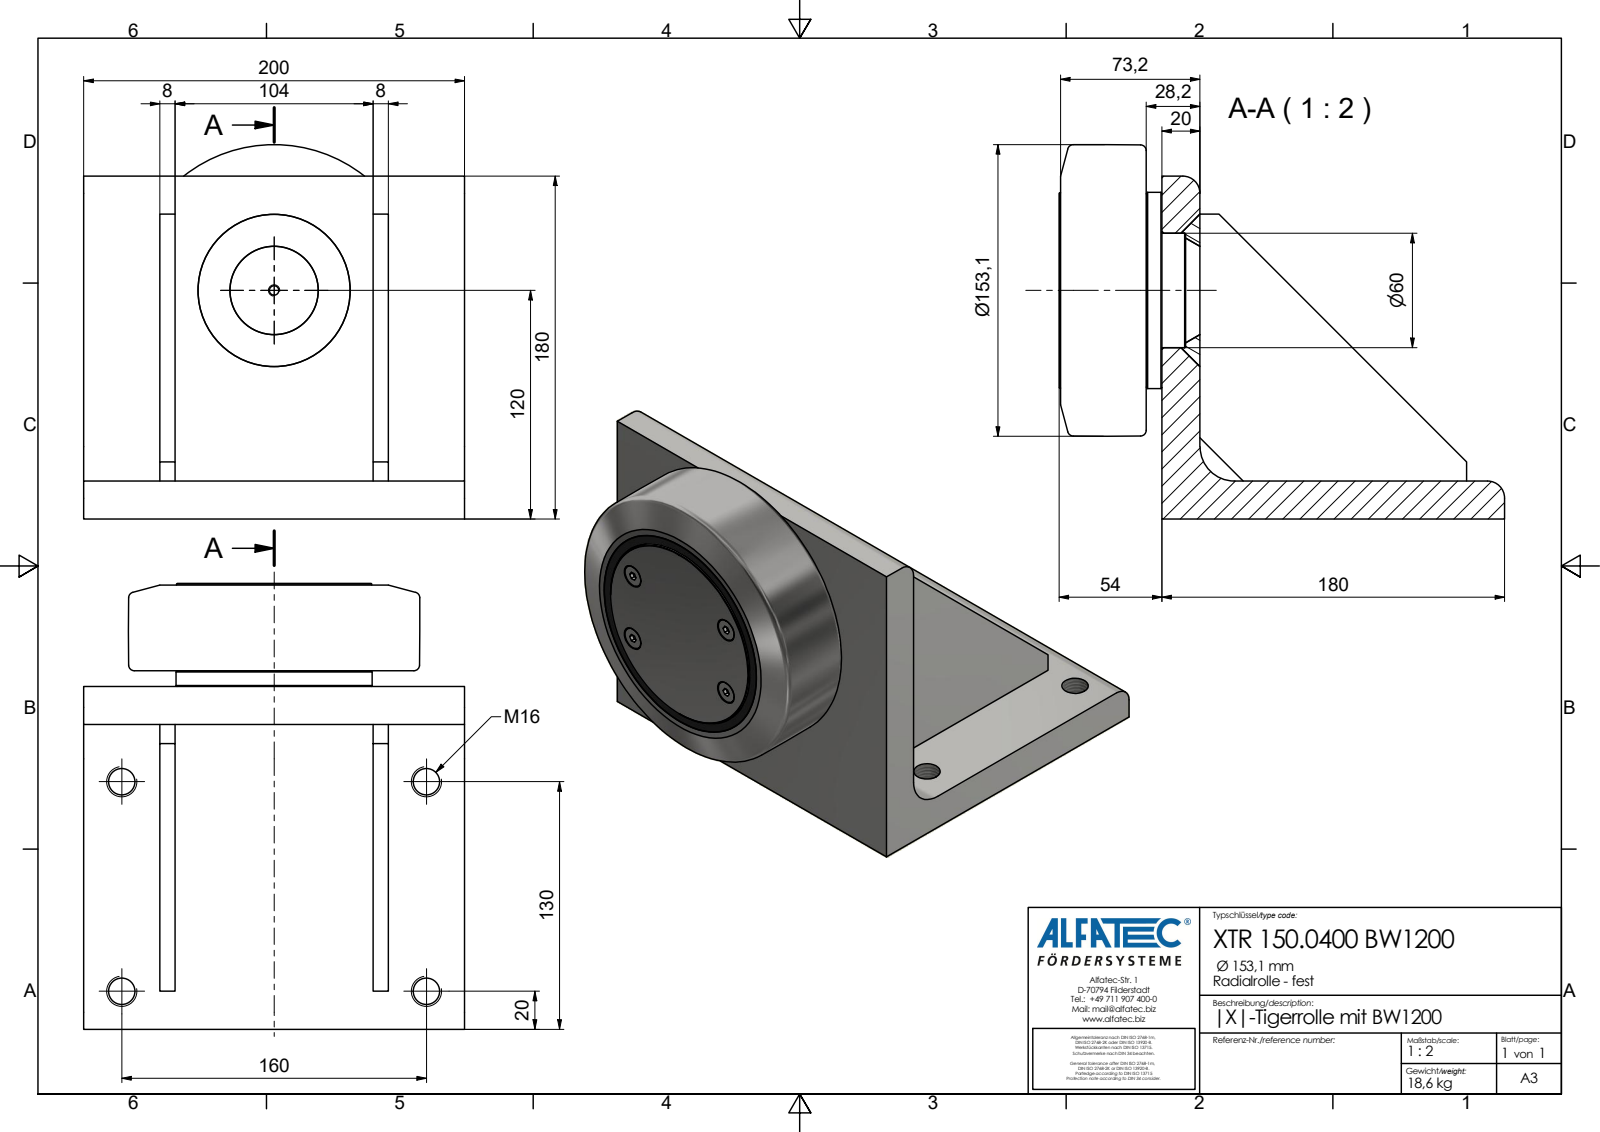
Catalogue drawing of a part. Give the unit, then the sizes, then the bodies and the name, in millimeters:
Units: millimetres
Overall size (bounding box): 234 × 200 × 196.55
Round holes (diameter × count): ⌀12.4 ×4, ⌀13.84 ×4
Round bosses / shafts (diameter × count): ⌀11.7 ×4, ⌀103 ×1, ⌀102.5 ×1, ⌀101.4 ×1
Partial cylindrical surfaces — rounded edges, fillets, slot ends (radius × count): R9 ×2, R18 ×1
Main face-to-face distances: 20, 8, 112, 160, 40, 48, 152, 104, 120, 8.2
Hole centre spacings: 40, 69.28, 80, 110, 160, 194.16
Volume: 2 414 000 mm³ · Surface area: 243 042 mm²
Bodies: 1 solid, 89 faces (60 planar, 18 cylindrical, 11 other)
Part name (STEP PRODUCT): XTR 150.0400 BW1200_Kontur
STEP written by: Autodesk Inventor 2020 (AP242_MANAGED_MODEL_BASED_3D_ENGINEERING_MIM_LF)
